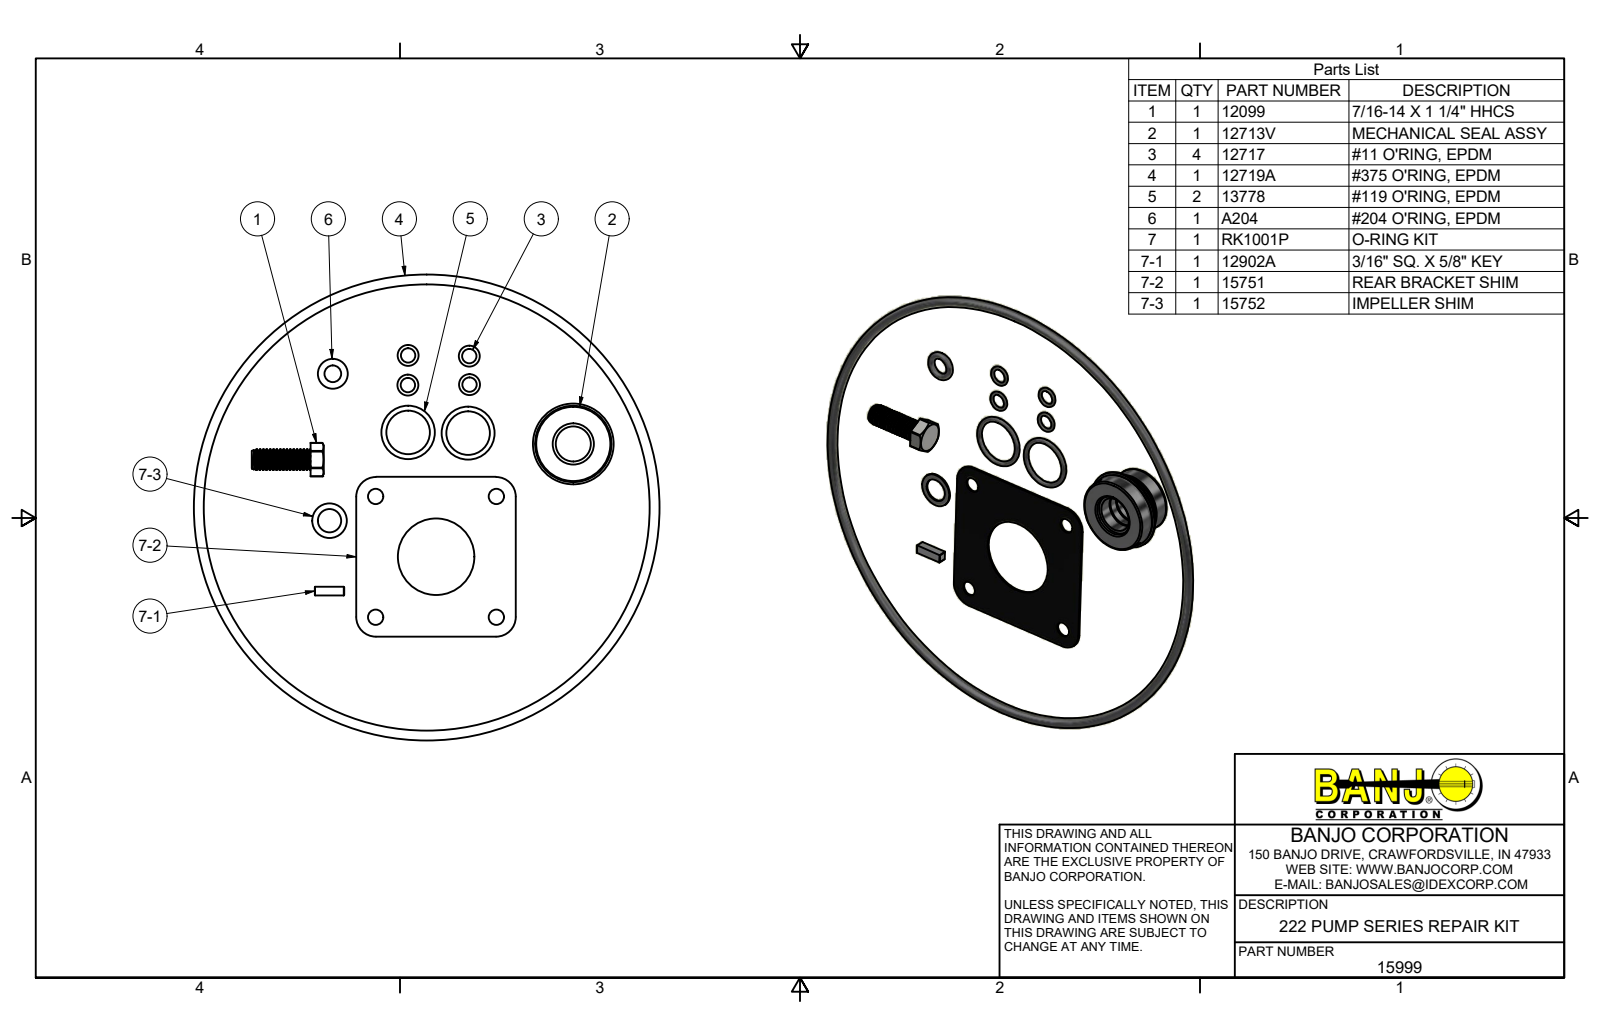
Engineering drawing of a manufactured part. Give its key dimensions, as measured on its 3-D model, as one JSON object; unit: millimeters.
{"part_name": "15999; RK1001P; 12902A; 15751 (+8 more)", "step_written_by": "Autodesk Inventor 2019 (AUTOMOTIVE_DESIGN)", "units": "millimeters", "bodies": {"solids": 14, "faces": 163, "planar": 43, "cylindrical": 66, "other": 54}, "overall_size": [251.3, 251.3, 25.9], "volume_mm3": 46930, "surface_area_mm2": 38840, "round_holes": [[8.2, 4], [12.7, 1], [19.1, 1], [20.7, 1], [22.2, 1], [25.4, 1], [41.4, 1]], "round_bosses_or_shafts": [[9.6, 17], [43.7, 1], [40, 1], [34.9, 1], [33.4, 1], [33.1, 1], [28.6, 1], [27, 1]], "partial_cylinders_radius": [[10.7, 4], [4.8, 1], [9, 1]], "face_to_face_distances": [0.8, 13.2, 14, 9.7, 3.6, 4.4, 11.9, 2.4, 15.6, 6], "hole_center_spacings": [65.1, 46.1, 92.1, 28.2, 46, 46.1, 50.2, 57.6]}
